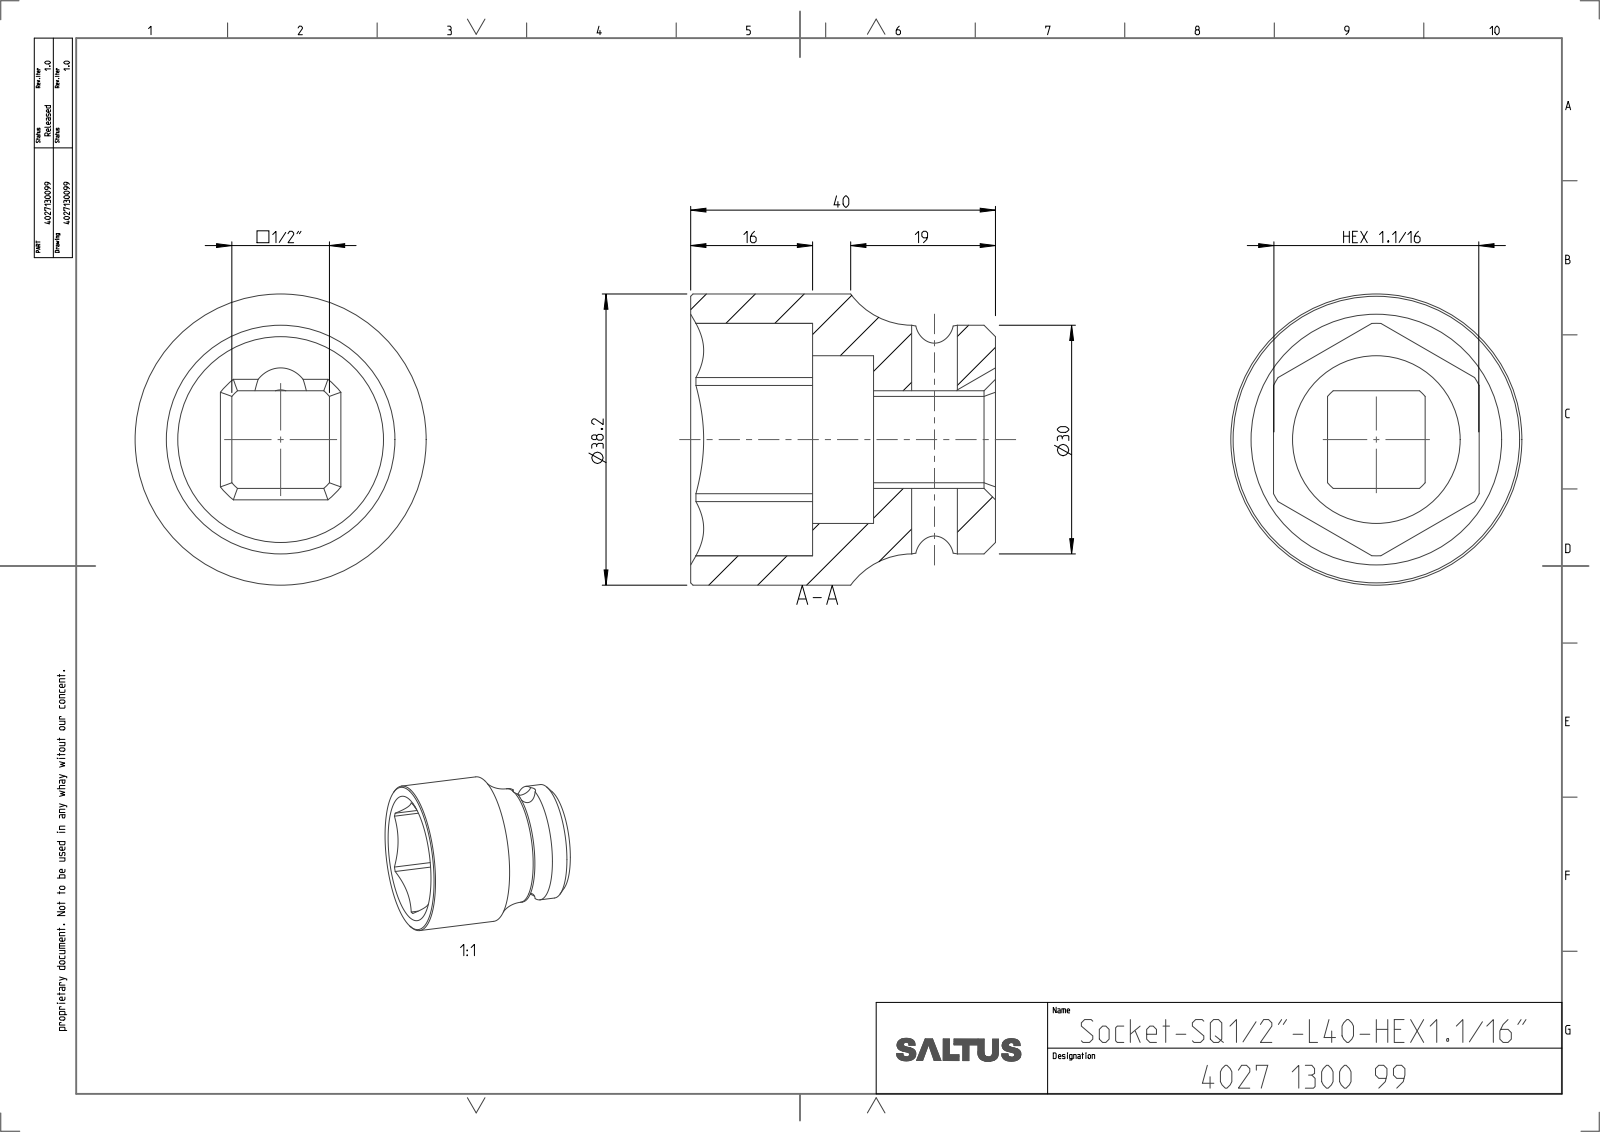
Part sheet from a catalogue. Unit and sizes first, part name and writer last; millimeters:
Units: millimetres
Overall size (bounding box): 40 × 38.2 × 38.2
Round holes (diameter × count): ⌀6 ×1, ⌀22 ×1
Round bosses / shafts (diameter × count): ⌀38.2 ×1, ⌀30 ×1
Partial cylindrical surfaces — rounded edges, fillets, slot ends (radius × count): R4 ×1, R8.55 ×1, R15.25 ×1
Main face-to-face distances: 26.98, 16, 24, 7.08, 19.9, 12.82, 40, 8
Volume: 21 384 mm³ · Surface area: 8 916 mm²
Bodies: 1 solid, 56 faces (19 planar, 23 cylindrical, 14 other)
Part name (STEP PRODUCT): 4027130099
STEP written by: CREO PARAMETRIC BY PTC INC, 2022414 (CONFIG_CONTROL_DESIGN)
